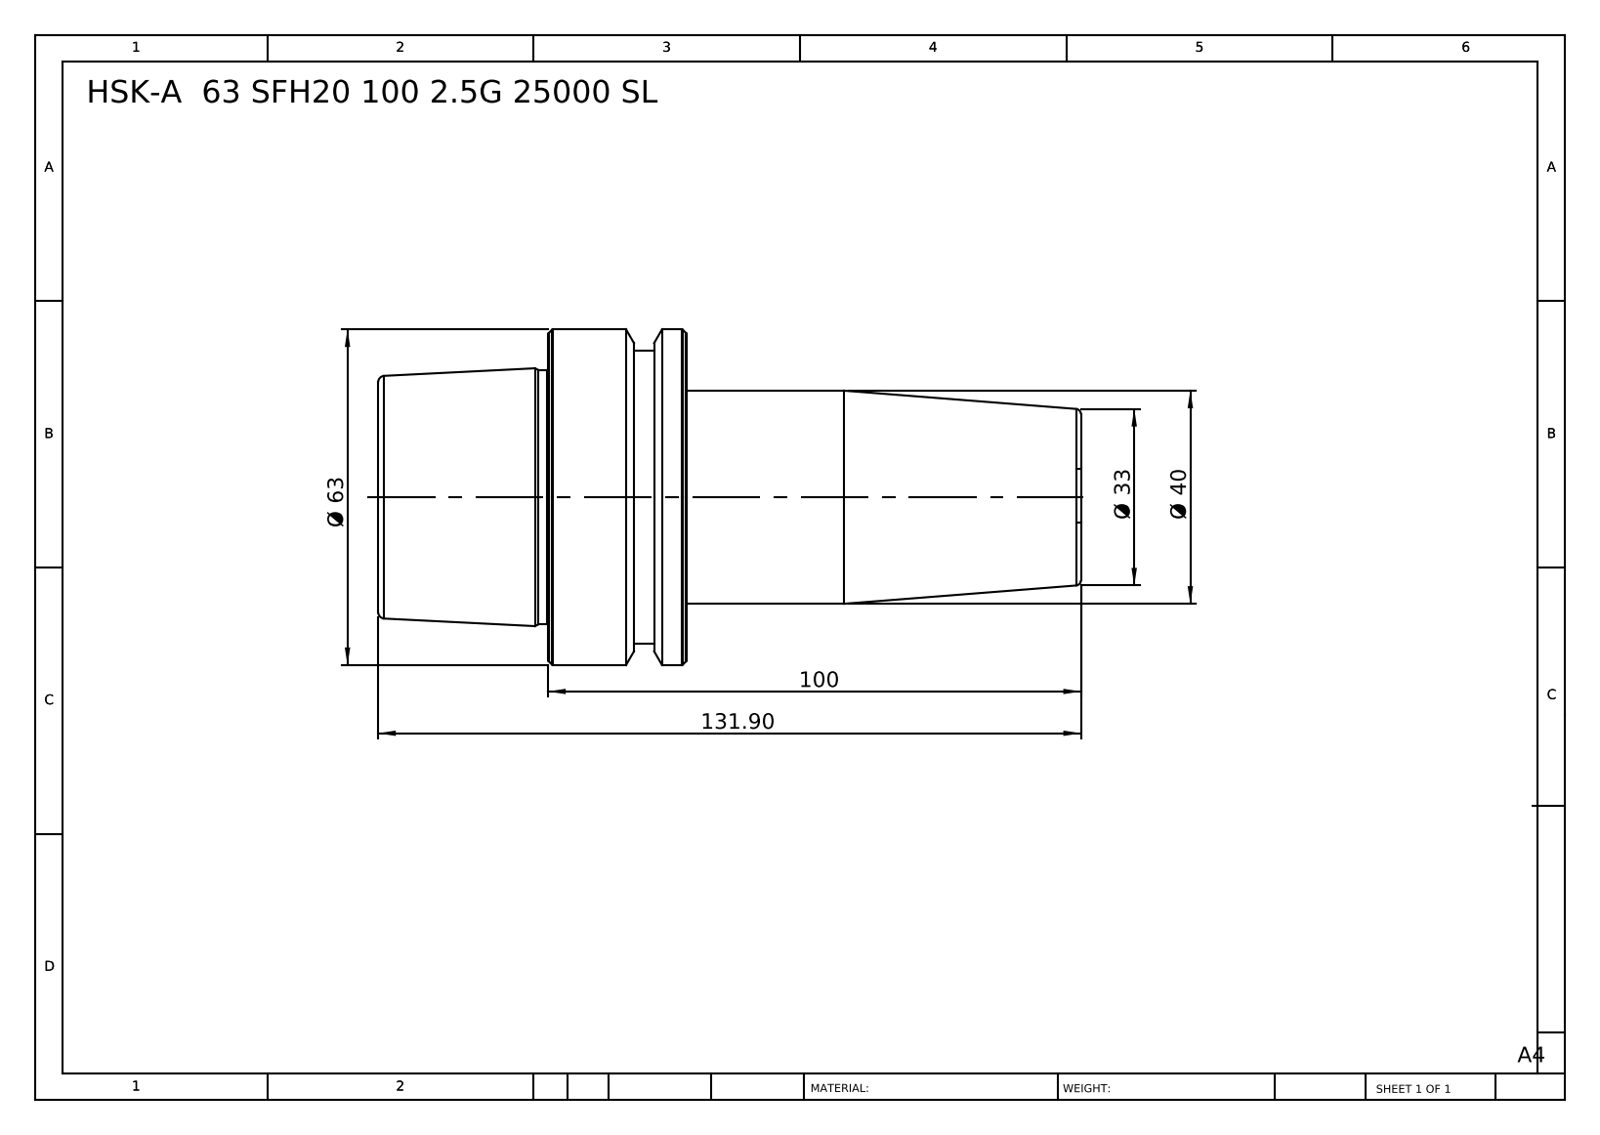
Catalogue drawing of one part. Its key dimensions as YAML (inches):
part_name: "HSK-A 63 SFH20 100 2.5G 25000 SL"
step_written_by: "SolidWorks 2014 (CONFIG_CONTROL_DESIGN)"
units: inches
bodies: {solids: 1, faces: 46, planar: 6, cylindrical: 10, other: 30}
overall_size: [5.193, 2.48, 2.48]
volume: 13.2
surface_area: 38.81
round_bosses_or_shafts:
  - {diameter: 2.48, count: 1}
  - {diameter: 2.165, count: 1}
  - {diameter: 1.881, count: 1}
  - {diameter: 1.575, count: 1}
face_to_face_distances: [2.28, 2.913, 5.193, 3.937, 1.024, 1.256, 3.154, 0.24, 0.783, 2.039]
